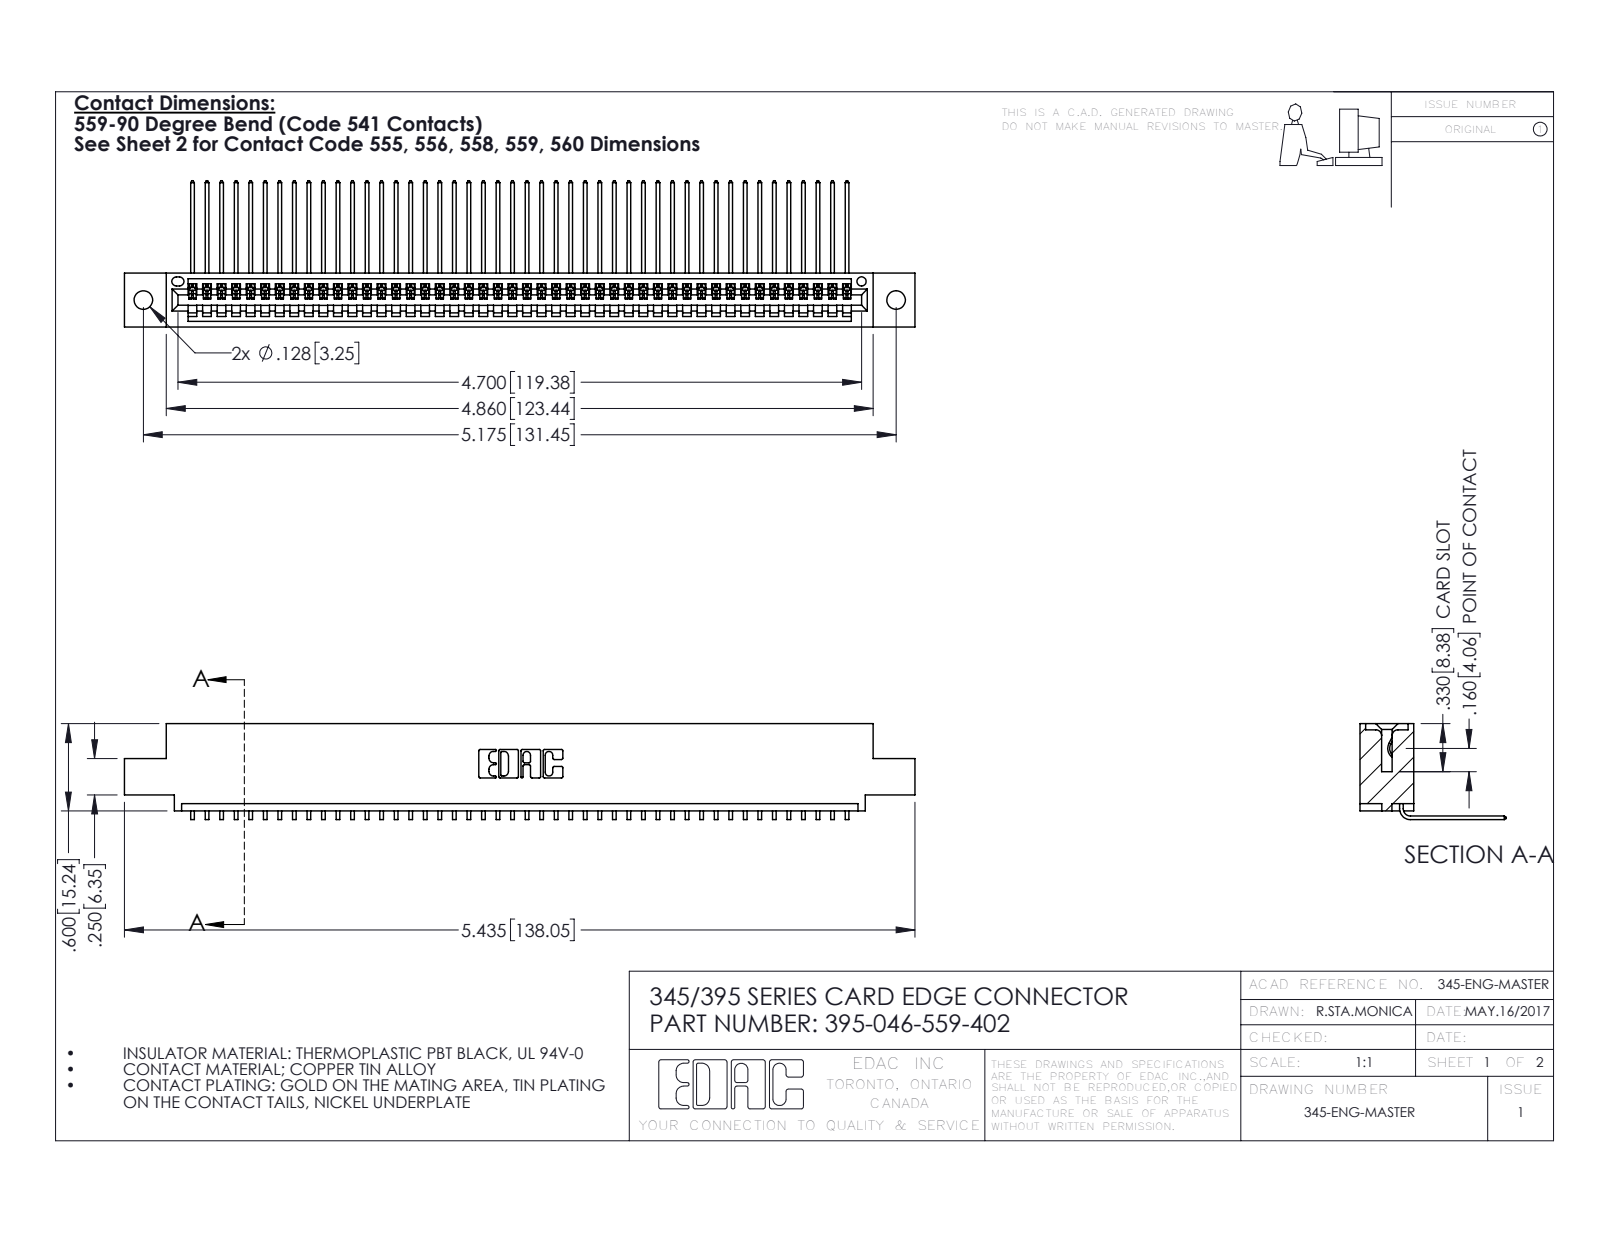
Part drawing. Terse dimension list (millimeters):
name: 395-046-559-402; 345 Part_0.110 Offset - 0.128 Dia; 345-292-001_558 559 Tail - 1
written by: SolidWorks 2016 (CONFIG_CONTROL_DESIGN)
unit: mm
bodies: 47 solids, 2890 faces (2016 planar, 874 cylindrical, 0 other)
size: 138 × 25.5 × 16.7
volume: 13 200 mm³; area: 18 290 mm²
holes: 2× ⌀3.3, 1× ⌀1.6
rounds: 92× R0.2, 22× R0.3, 6× R0.2, 6× R0.8, 3× R0.7, 2× R0.8, 2× R1, 1× R0.4
face distances: 1.8, 7.6, 9.4, 5.1, 2.5, 6.9, 0.6, 5.7, 3.8, 1.8
hole spacings: 6.9, 125.5, 131.4
